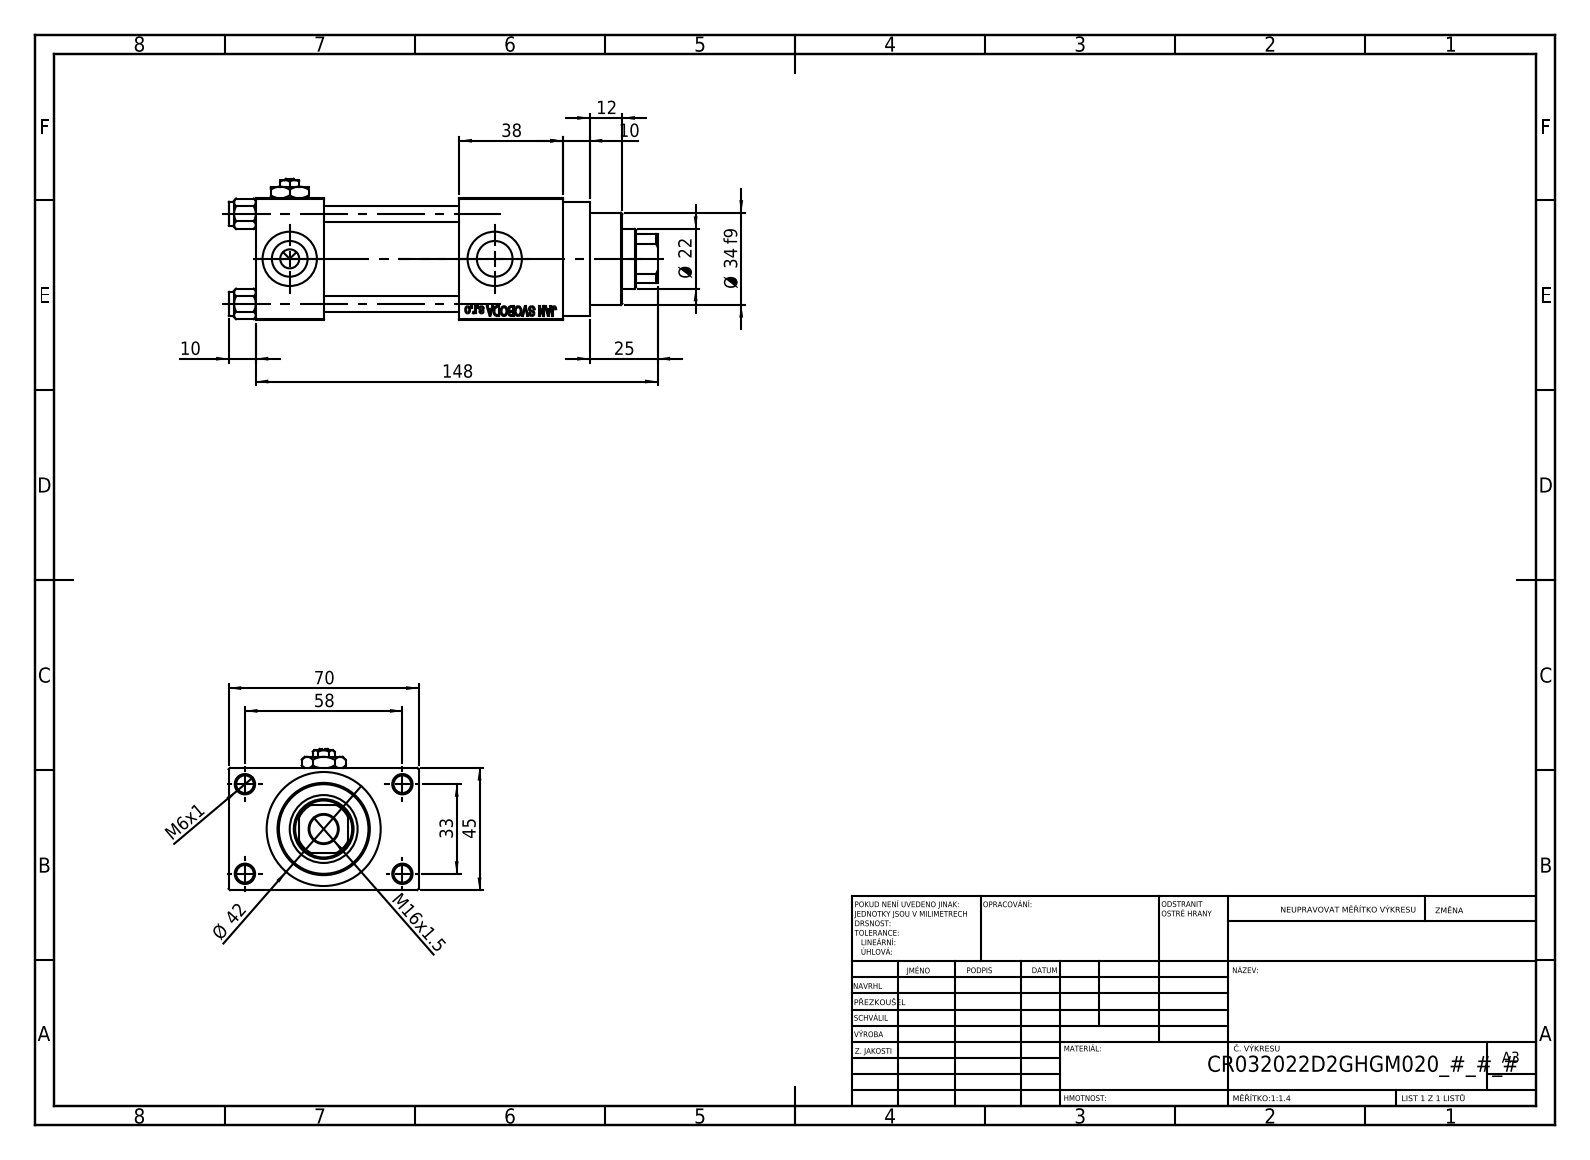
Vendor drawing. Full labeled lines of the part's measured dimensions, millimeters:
Part name (STEP PRODUCT): V215_VC_A; V215CR_VCP_D; V215CR_D_Body; V215CR_D_TYCINKA (+2 more)
STEP written by: SolidWorks 2019 (CONFIG_CONTROL_DESIGN)
Units: millimetres
Bodies: 12 solids, 1154 faces (519 planar, 95 cylindrical, 540 other)
Overall size (bounding box): 158 × 70 × 52
Volume: 241 822 mm³ · Surface area: 81 111 mm²
Round holes (diameter × count): ⌀6 ×4, ⌀6.5 ×4, ⌀7 ×3, ⌀13.16 ×3, ⌀20 ×3, ⌀10.5 ×1, ⌀22 ×1, ⌀24 ×1, ⌀25 ×1, ⌀32 ×1, ⌀33 ×1
Round bosses / shafts (diameter × count): ⌀9 ×4, ⌀42 ×1, ⌀38 ×1, ⌀34 ×1
Partial cylindrical surfaces — rounded edges, fillets, slot ends (radius × count): R10.5 ×1
Main face-to-face distances: 45, 25, 50, 12.5, 75, 57.5, 88, 38, 113, 70
Hole centre spacings: 12.4, 23.48, 33.2, 33.37, 35.35, 45.6, 56.35, 33
